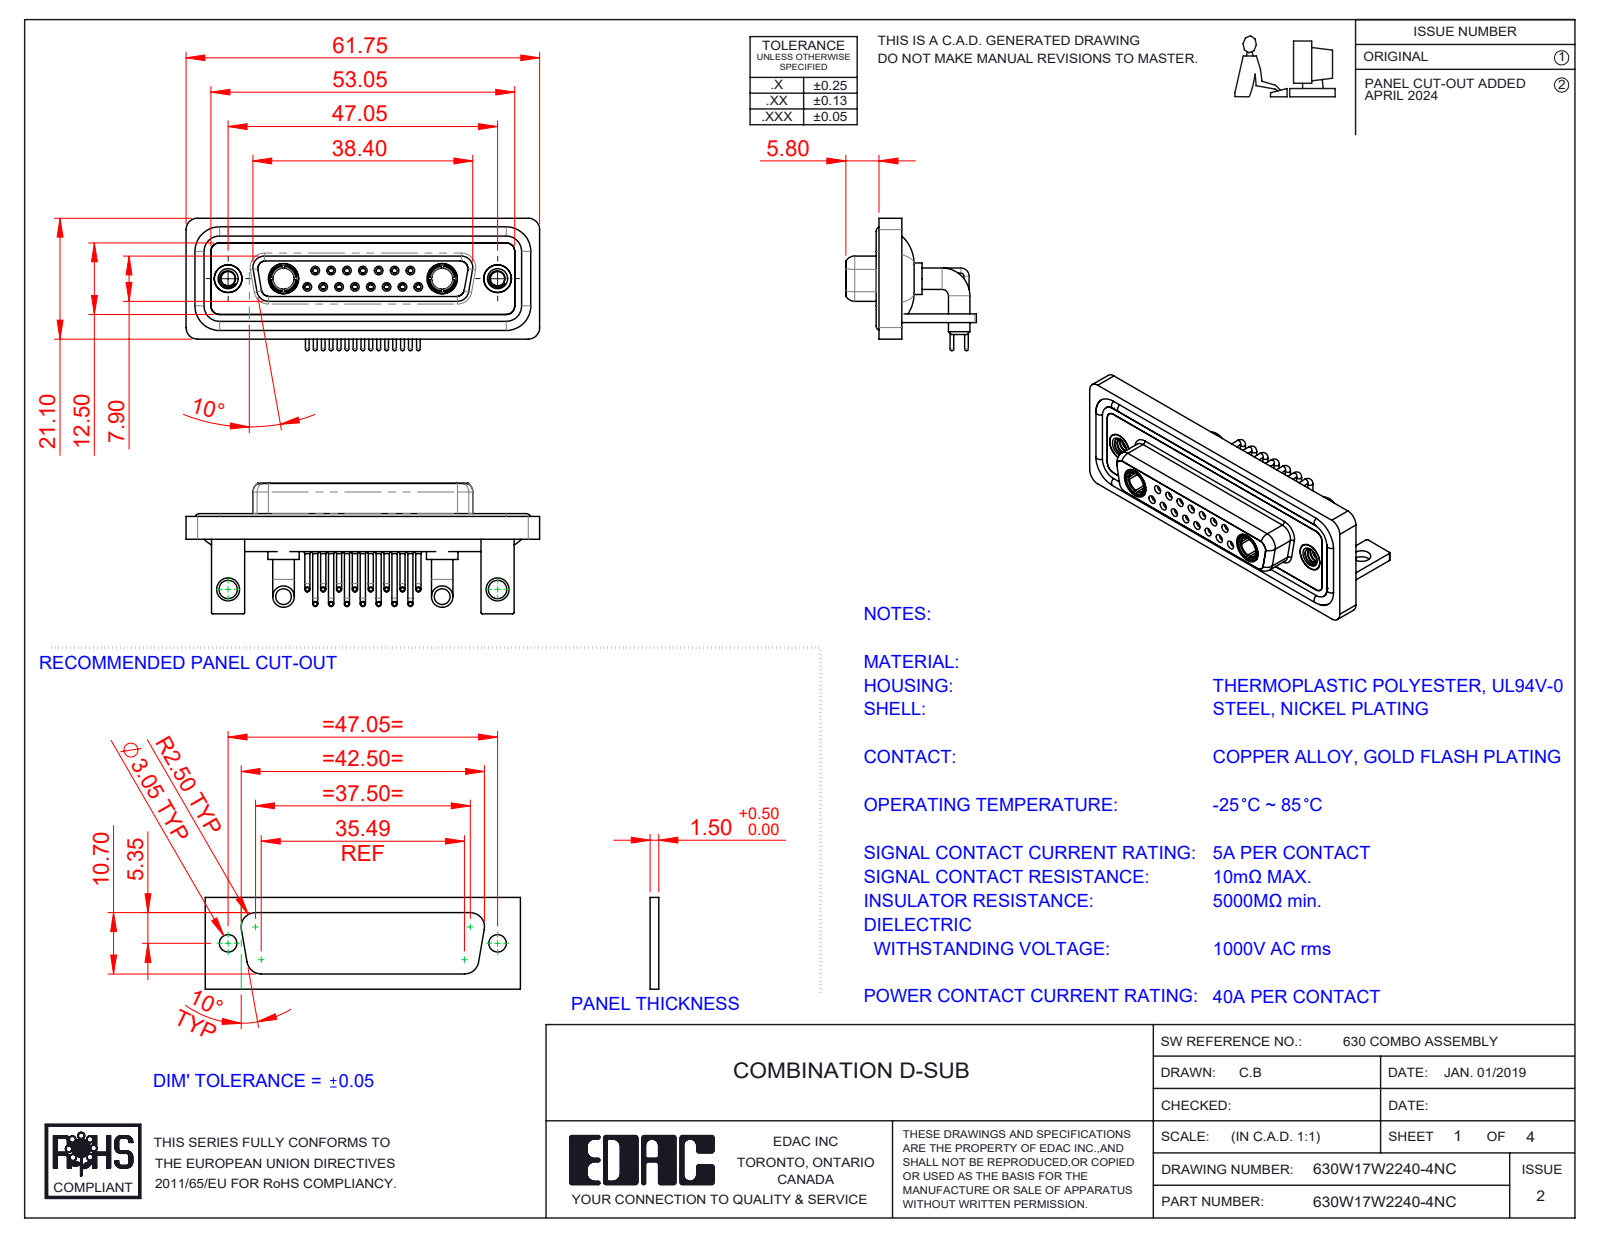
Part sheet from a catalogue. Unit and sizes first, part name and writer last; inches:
Units: inches
Overall size (bounding box): 2.431 × 0.91 × 0.898
Round holes (diameter × count): ⌀0.035 ×15, ⌀0.043 ×15, ⌀0.059 ×15, ⌀0.079 ×15, ⌀0.063 ×8, ⌀0.067 ×7, ⌀0.191 ×4, ⌀0.098 ×2, ⌀0.126 ×2, ⌀0.146 ×2, ⌀0.157 ×2, ⌀0.159 ×2
Round bosses / shafts (diameter × count): ⌀0.035 ×15, ⌀0.026 ×15, ⌀0.063 ×11, ⌀0.148 ×4, ⌀0.217 ×2, ⌀0.205 ×2, ⌀0.195 ×2, ⌀0.195 ×2
Partial cylindrical surfaces — rounded edges, fillets, slot ends (radius × count): R0.079 ×19, R0.059 ×18, R0.01 ×16, R0.053 ×8, R0.063 ×8, R0.02 ×5, R0.024 ×4, R0.026 ×4
Main face-to-face distances: 0.016, 0.071, 0.114, 0.146, 0.059, 0.161, 0.043, 0.055, 0.063, 0.122
Hole centre spacings: 0.124, 0.109, 0.218, 0.327, 0.198, 0.295, 0.436, 0.198
Volume: 0.549 in³ · Surface area: 23.8 in²
Bodies: 28 solids, 1379 faces (408 planar, 605 cylindrical, 366 other)
Part name (STEP PRODUCT): 630Combo Contact Row 2_50 Contacts; 630Combo Shell Rear_25 Contacts; 630Combo Waterproof Housing_25 Contacts; 630W17W2240-4NC (+6 more)
STEP written by: SolidWorks 2023 (CONFIG_CONTROL_DESIGN)
